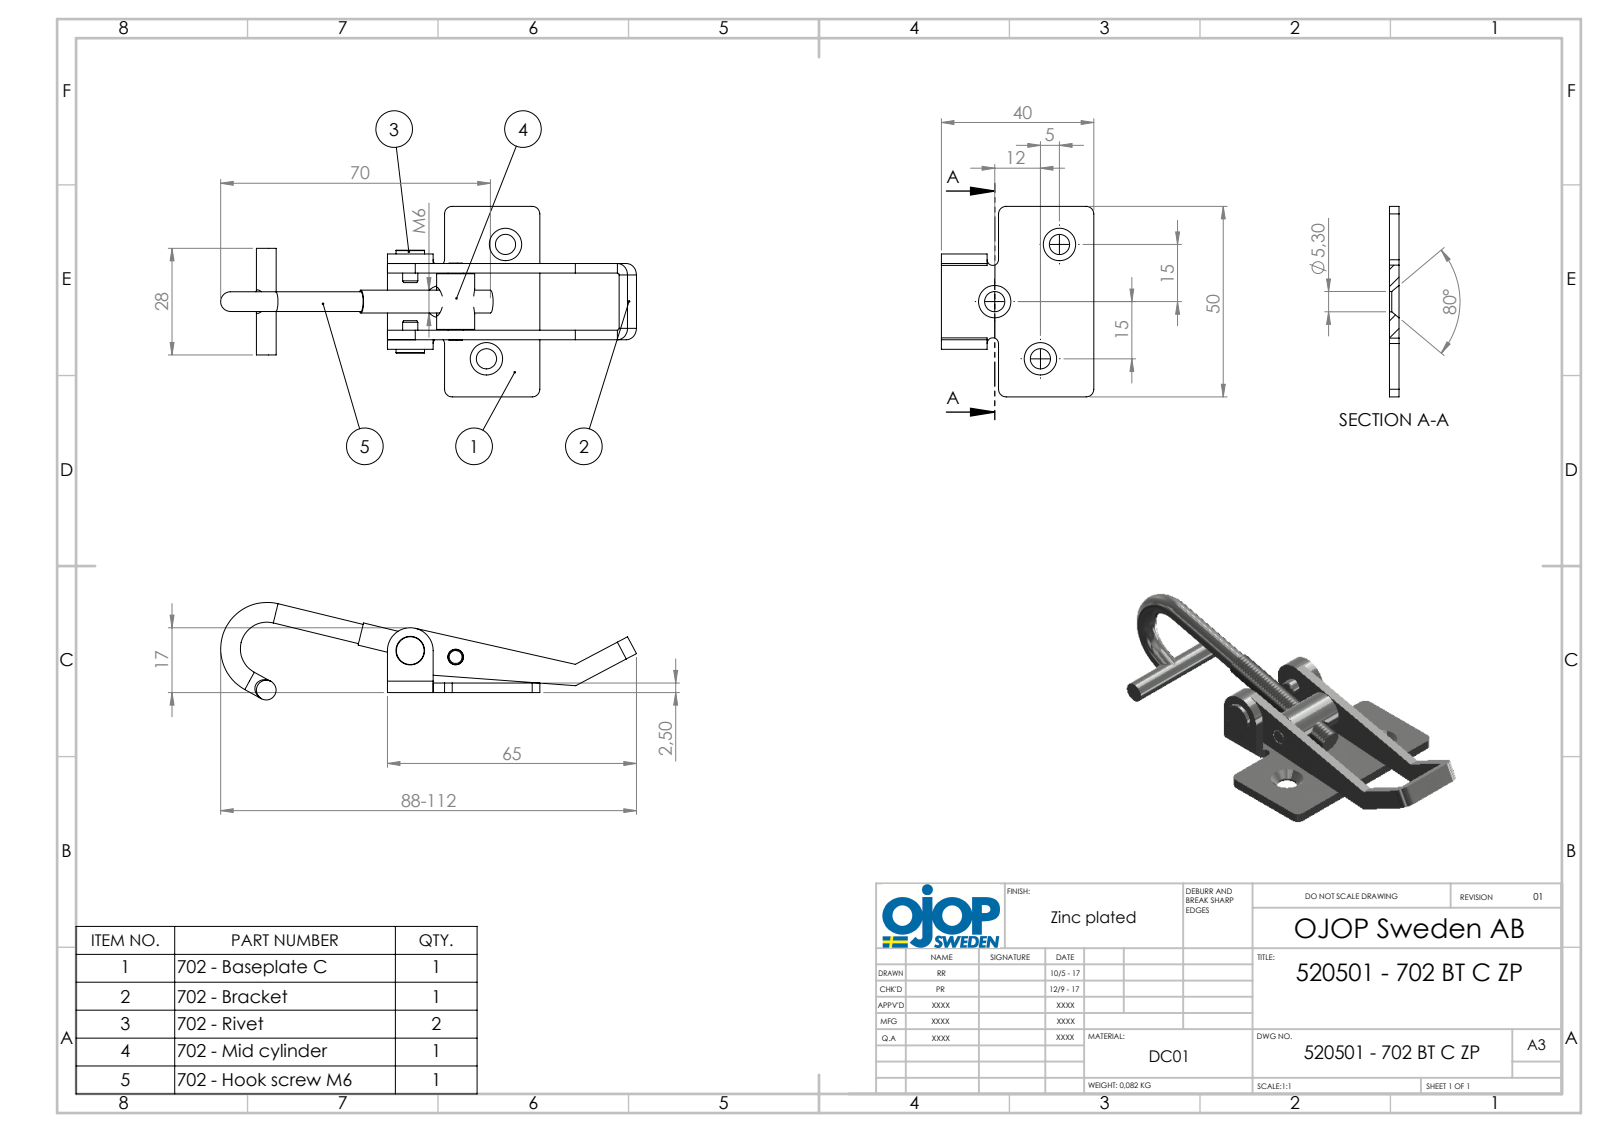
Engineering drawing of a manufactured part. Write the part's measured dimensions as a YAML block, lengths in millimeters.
part_name: "702 - Bygel; 702 - Böjd T-skruv M6; 702 - C; 702 - Ansatsnit (+2 more)"
step_written_by: "SolidWorks 2015 (AUTOMOTIVE_DESIGN)"
units: millimeters
bodies: {solids: 6, faces: 149, planar: 58, cylindrical: 65, other: 26}
overall_size: [108.61, 50, 25.57]
volume: 11107
surface_area: 10617
round_holes:
  - {diameter: 5.3, count: 3}
  - {diameter: 4.1, count: 2}
  - {diameter: 5, count: 1}
  - {diameter: 6, count: 1}
round_bosses_or_shafts:
  - {diameter: 5.18, count: 3}
  - {diameter: 4, count: 2}
  - {diameter: 10, count: 1}
  - {diameter: 7.5, count: 1}
  - {diameter: 6, count: 1}
partial_cylinders:
  - {radius: 0.5, count: 4}
  - {radius: 2, count: 4}
  - {radius: 3, count: 4}
  - {radius: 1.5, count: 2}
  - {radius: 6, count: 1}
face_to_face_distances: [2.5, 17.5, 20, 15, 5, 22.5, 25, 19.8, 5.2, 2.7]
hole_center_spacings: [12.03, 19.21, 22.67, 30.41]
